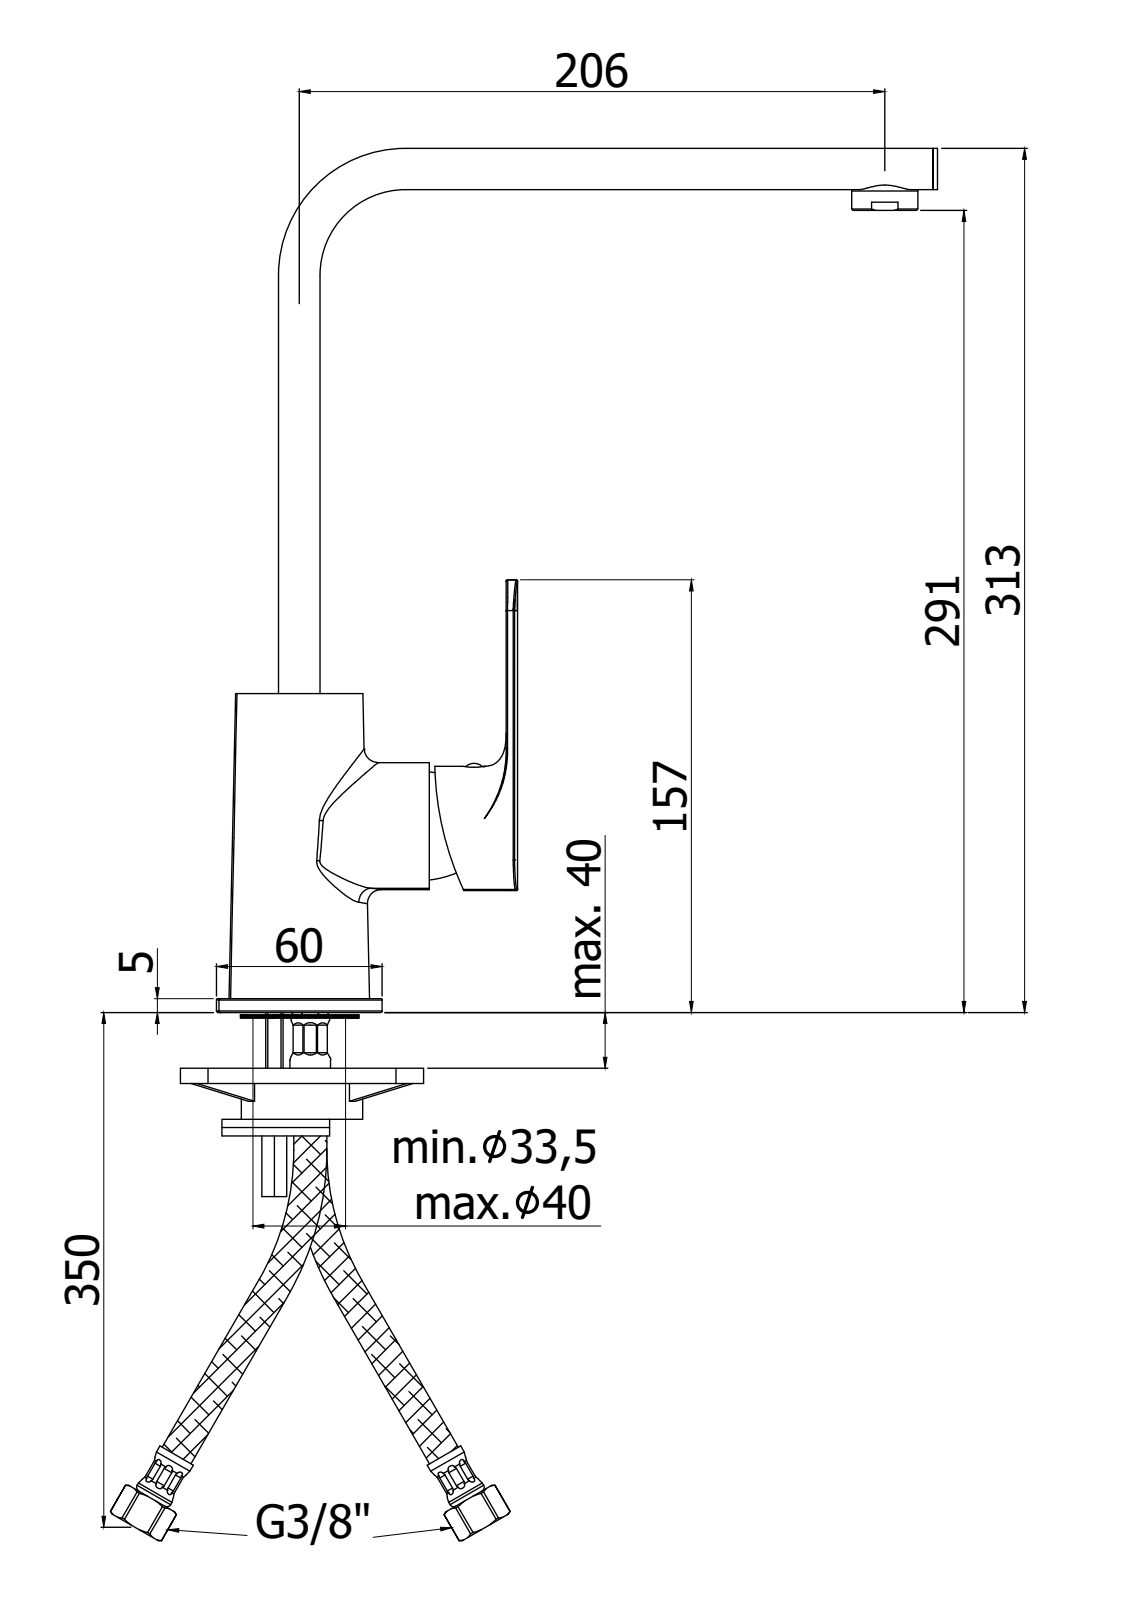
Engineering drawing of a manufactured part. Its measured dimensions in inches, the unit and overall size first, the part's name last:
Units: inches
Overall size (bounding box): 12.323 × 10.242 × 4.289
Round holes (diameter × count): ⌀0.276 ×4, ⌀0.217 ×3, ⌀0.354 ×3, ⌀0.433 ×3, ⌀0.197 ×2, ⌀0.315 ×2, ⌀1.496 ×2, ⌀1.575 ×2, ⌀0.118 ×1, ⌀0.134 ×1, ⌀0.138 ×1, ⌀0.157 ×1
Round bosses / shafts (diameter × count): ⌀0.189 ×2, ⌀0.157 ×2, ⌀1.752 ×1, ⌀1.567 ×1, ⌀1.449 ×1, ⌀1.394 ×1, ⌀1.378 ×1, ⌀1.291 ×1
Partial cylindrical surfaces — rounded edges, fillets, slot ends (radius × count): R0.02 ×44, R0.059 ×13, R0.039 ×10, R0.118 ×10, R0.067 ×6, R0.079 ×5, R0.008 ×4, R0.031 ×4
Main face-to-face distances: 0.059, 0.531, 0.472, 0.591, 0.217, 0.087, 0.197, 0.079, 11.732, 11.791
Hole centre spacings: 0.335, 0.339, 0.378, 0.53, 0.559, 0.596, 0.606, 0.864
Volume: 17.07 in³ · Surface area: 235 in²
Bodies: 2 solids, 3364 faces (2422 planar, 533 cylindrical, 409 other)
Part name (STEP PRODUCT): SY180CR
STEP written by: CREO PARAMETRIC BY PTC INC, 2020044 (CONFIG_CONTROL_DESIGN)
